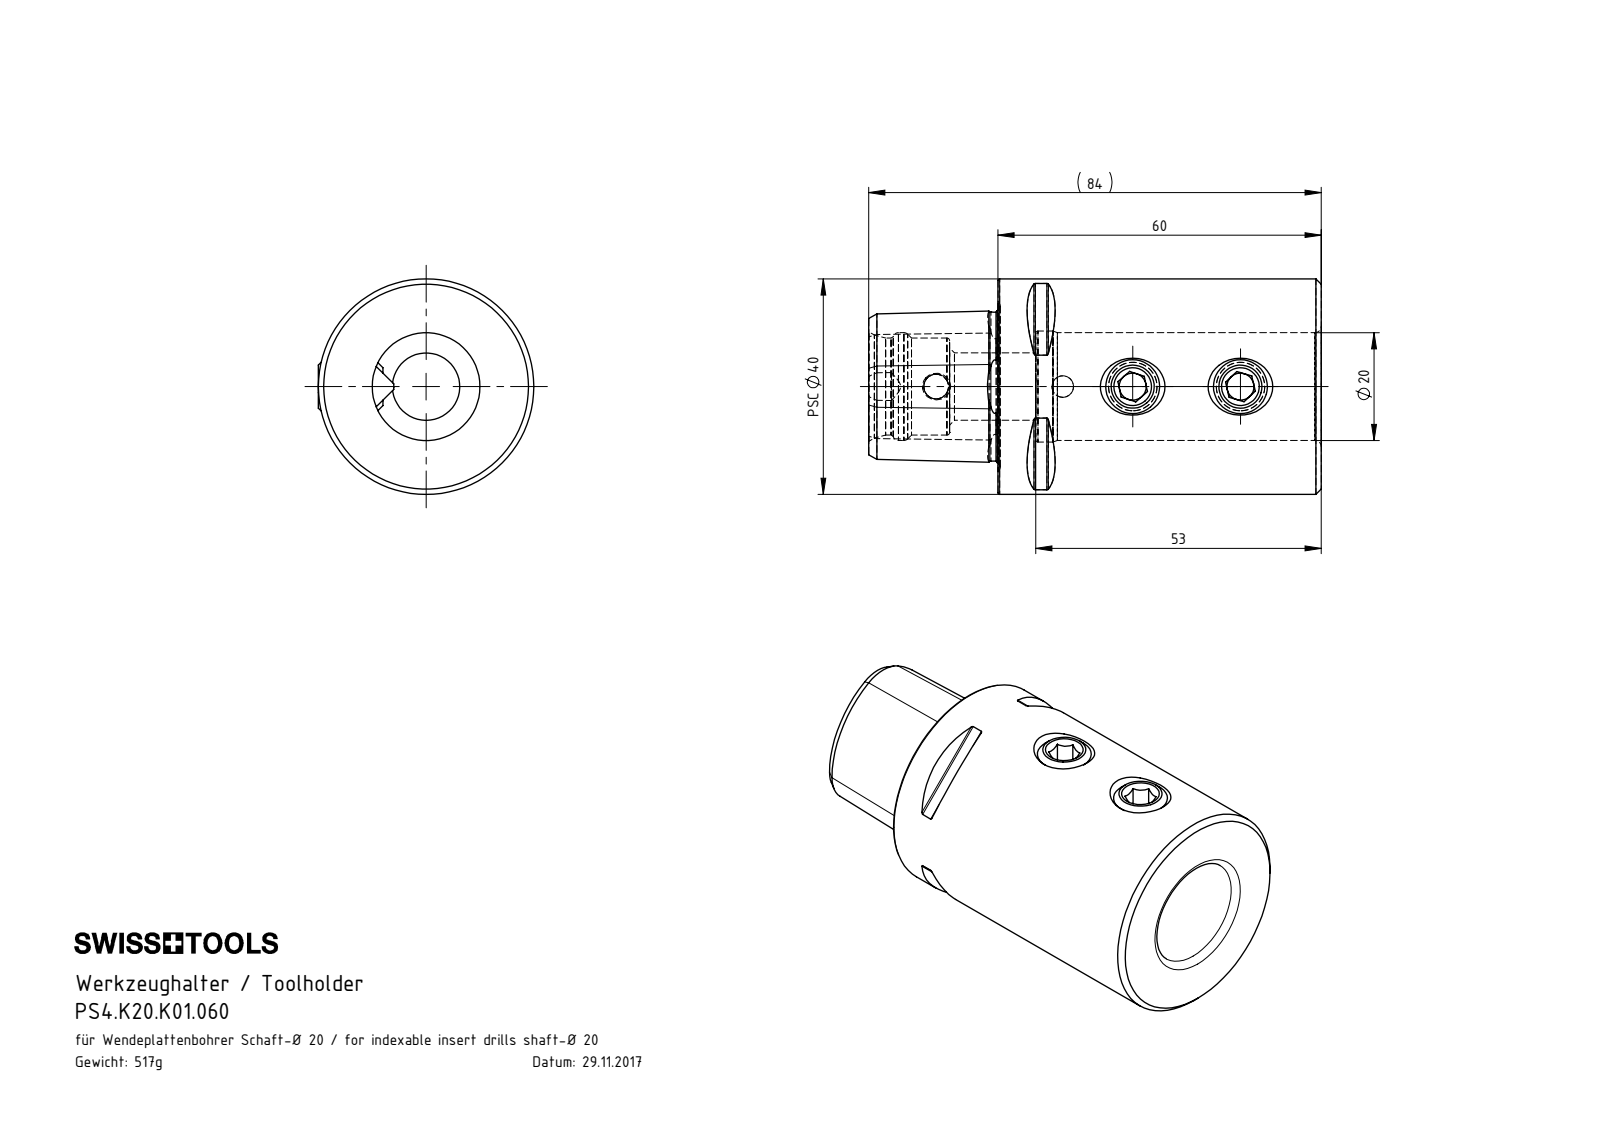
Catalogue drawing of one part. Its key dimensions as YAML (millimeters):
part_name: "PS4.K20.K01.060; K20-ER2.010.014_PreviewCfg; PS4-K20.K01.060_A; K20-ER1.010.012_PreviewCfg"
step_written_by: "SolidWorks 2017 (AUTOMOTIVE_DESIGN)"
units: millimeters
bodies: {solids: 3, faces: 141, planar: 48, cylindrical: 25, other: 68}
overall_size: [84, 40, 40]
volume: 65899
surface_area: 18226
round_holes:
  - {diameter: 5, count: 2}
  - {diameter: 9, count: 2}
  - {diameter: 4, count: 1}
  - {diameter: 4.6, count: 1}
  - {diameter: 12.5, count: 1}
  - {diameter: 18, count: 1}
  - {diameter: 20, count: 1}
  - {diameter: 20.6, count: 1}
round_bosses_or_shafts:
  - {diameter: 10, count: 2}
  - {diameter: 40, count: 1}
partial_cylinders:
  - {radius: 0.3, count: 8}
  - {radius: 3, count: 1}
face_to_face_distances: [60, 7, 53, 24, 31, 84, 15.52, 35.3, 9, 15]
hole_center_spacings: [13, 20, 23.5, 33, 36.5, 56.5]
